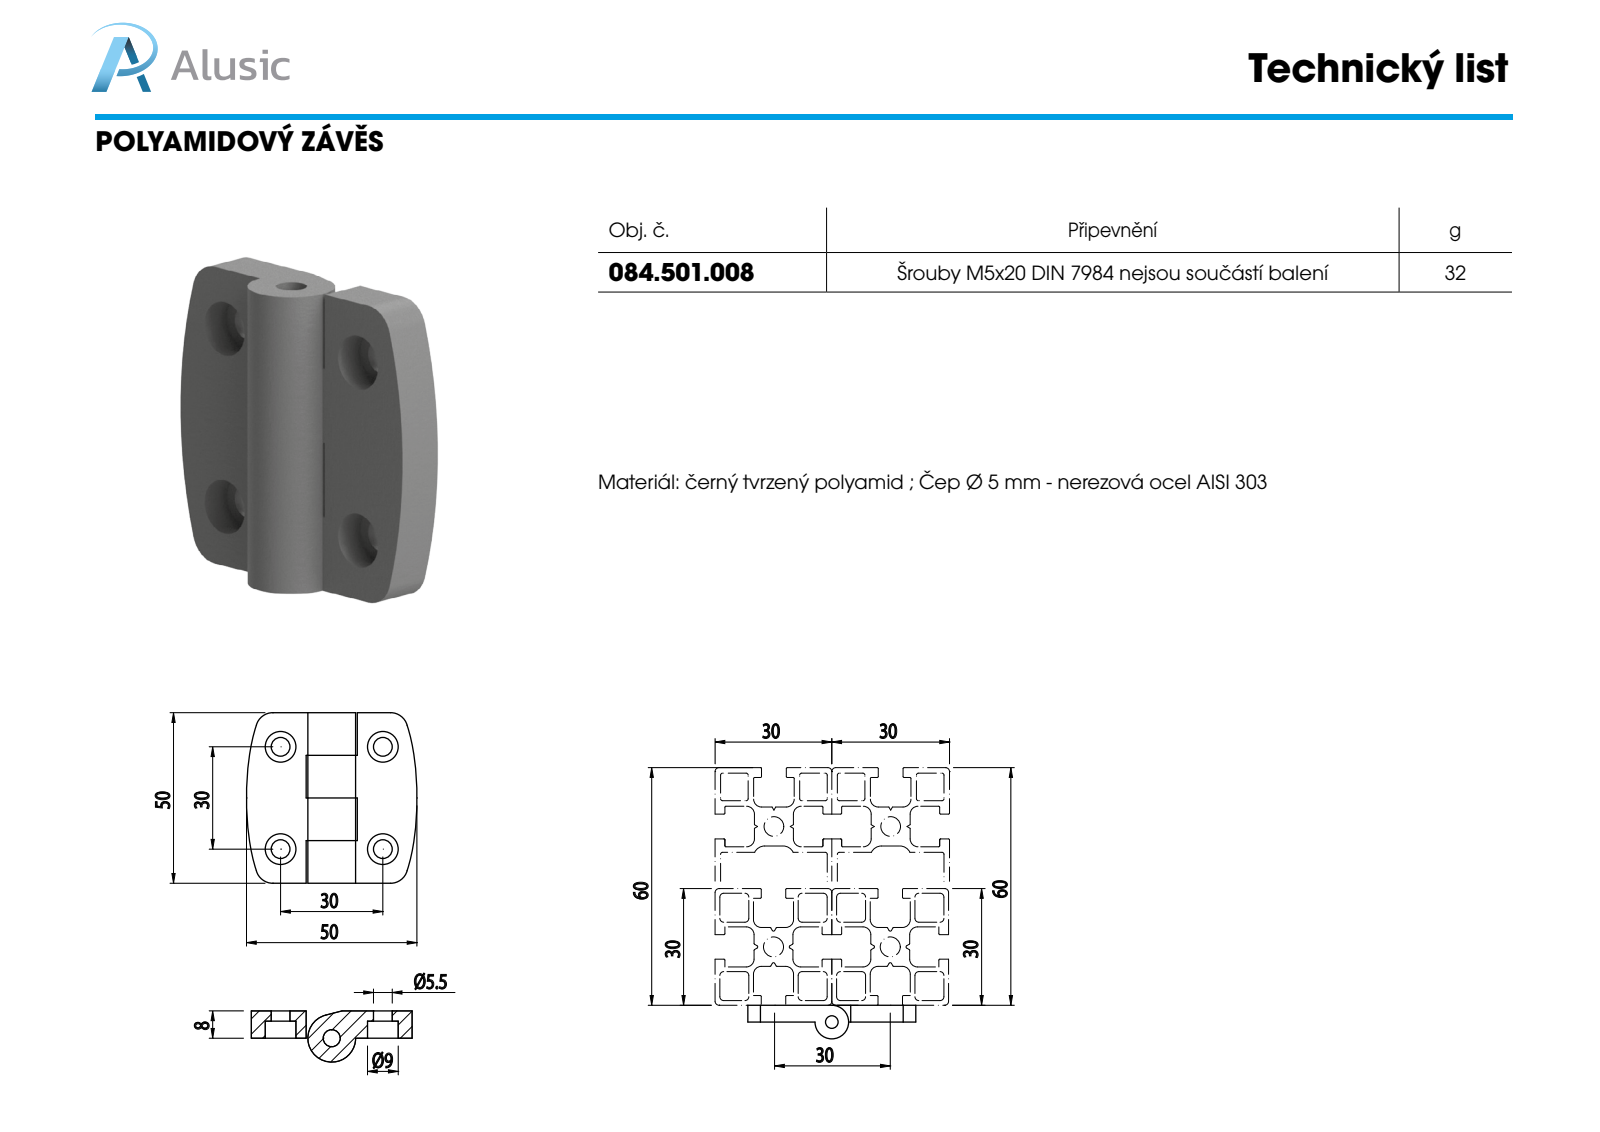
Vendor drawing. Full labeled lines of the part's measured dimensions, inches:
Part name (STEP PRODUCT): 084.501.008; 084.501.008 ALETTA
STEP written by: SolidWorks 2011 (CONFIG_CONTROL_DESIGN)
Units: inches
Bodies: 2 solids, 60 faces (26 planar, 34 cylindrical, 0 other)
Overall size (bounding box): 1.969 × 1.969 × 0.591
Volume: 1.162 in³ · Surface area: 14.71 in²
Round holes (diameter × count): ⌀0.217 ×4, ⌀0.354 ×4, ⌀0.197 ×1
Round bosses / shafts (diameter × count): ⌀0.551 ×1
Partial cylindrical surfaces — rounded edges, fillets, slot ends (radius × count): R0.197 ×4, R3.15 ×2
Main face-to-face distances: 0.315, 0.492, 0.984, 1.476, 1.969, 0.591, 0.118, 0.197
Hole centre spacings: 1.181, 1.67
